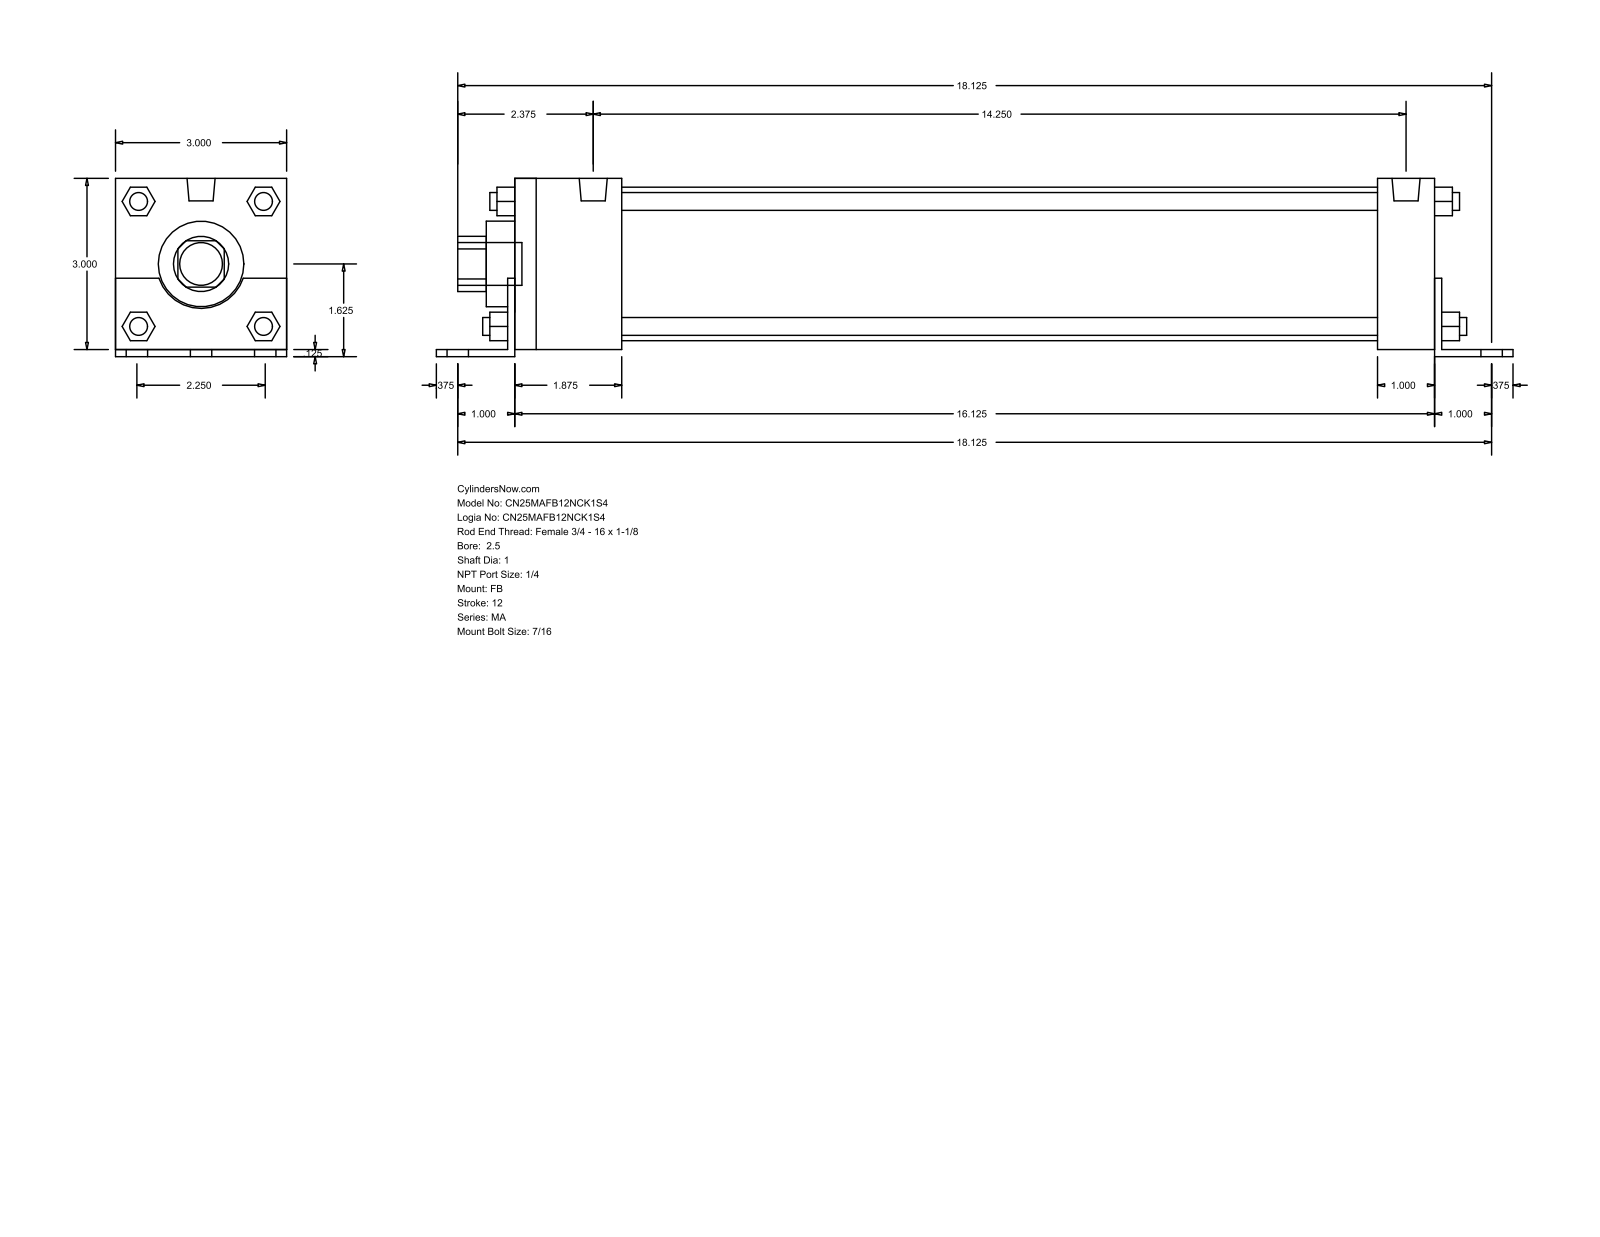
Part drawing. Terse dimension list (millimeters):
name: MA_FB__0250_1
written by: GSSL Pune (CONFIG_CONTROL_DESIGN)
unit: mm
bodies: 0 solids, 140 faces (105 planar, 35 cylindrical, 0 other)
size: 479.43 × 79.38 × 76.2
holes: 1× ⌀25.4, 1× ⌀38.1, 1× ⌀68.33
bosses: 8× ⌀7.94, 6× ⌀11.11, 2× ⌀12.49, 1× ⌀19.05
rounds: 1× R12.29, 1× R19.81
face distances: 76.2, 3.17, 79.37, 412.75, 409.58, 12.7, 47.63, 361.95, 365.12, 384.17
